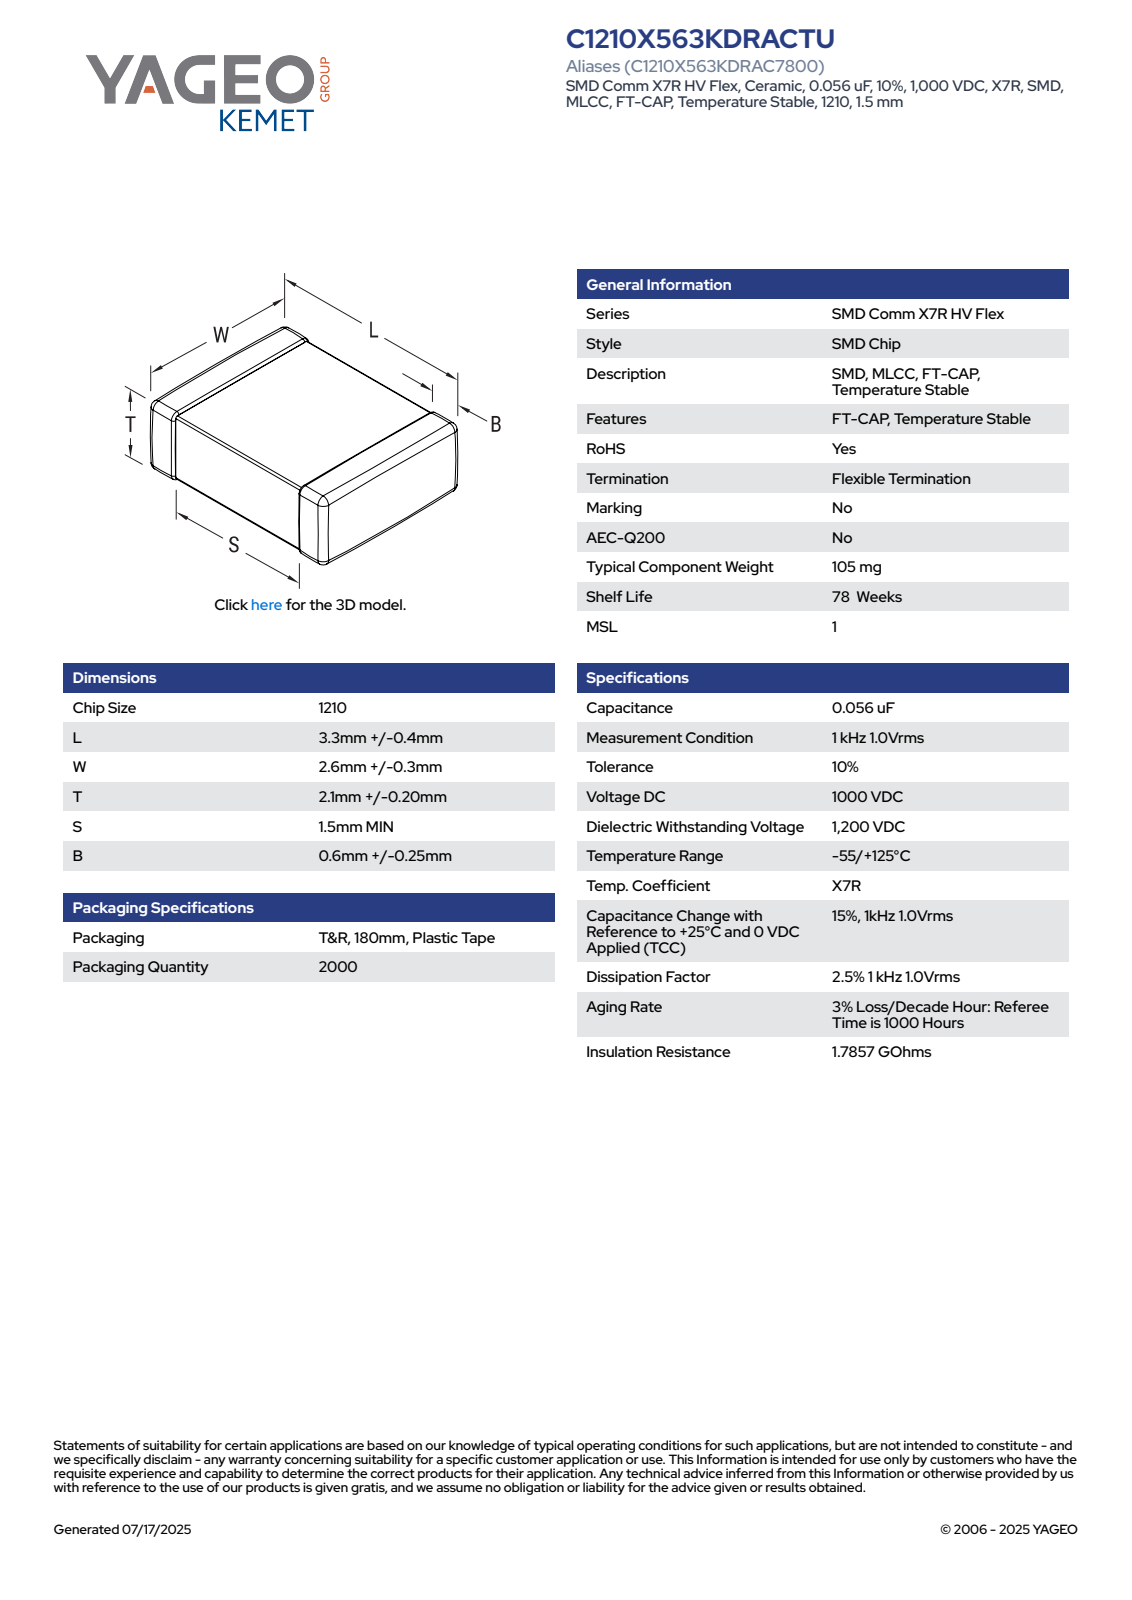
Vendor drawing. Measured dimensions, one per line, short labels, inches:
name: CCS_CCSTD_1210_L3.7W2.9T2.3B0.6
written by: SolidWorks 2021 (AUTOMOTIVE_DESIGN)
unit: in
bodies: 4 solids, 129 faces (71 planar, 42 cylindrical, 16 other)
size: 0.146 × 0.114 × 0.091
volume: 0.001 in³; area: 0.081 in²
face distances: 0.088, 0.112, 0.146, 0.086, 0.109, 0.091, 0.114, 0.017, 0.062, 0.084
